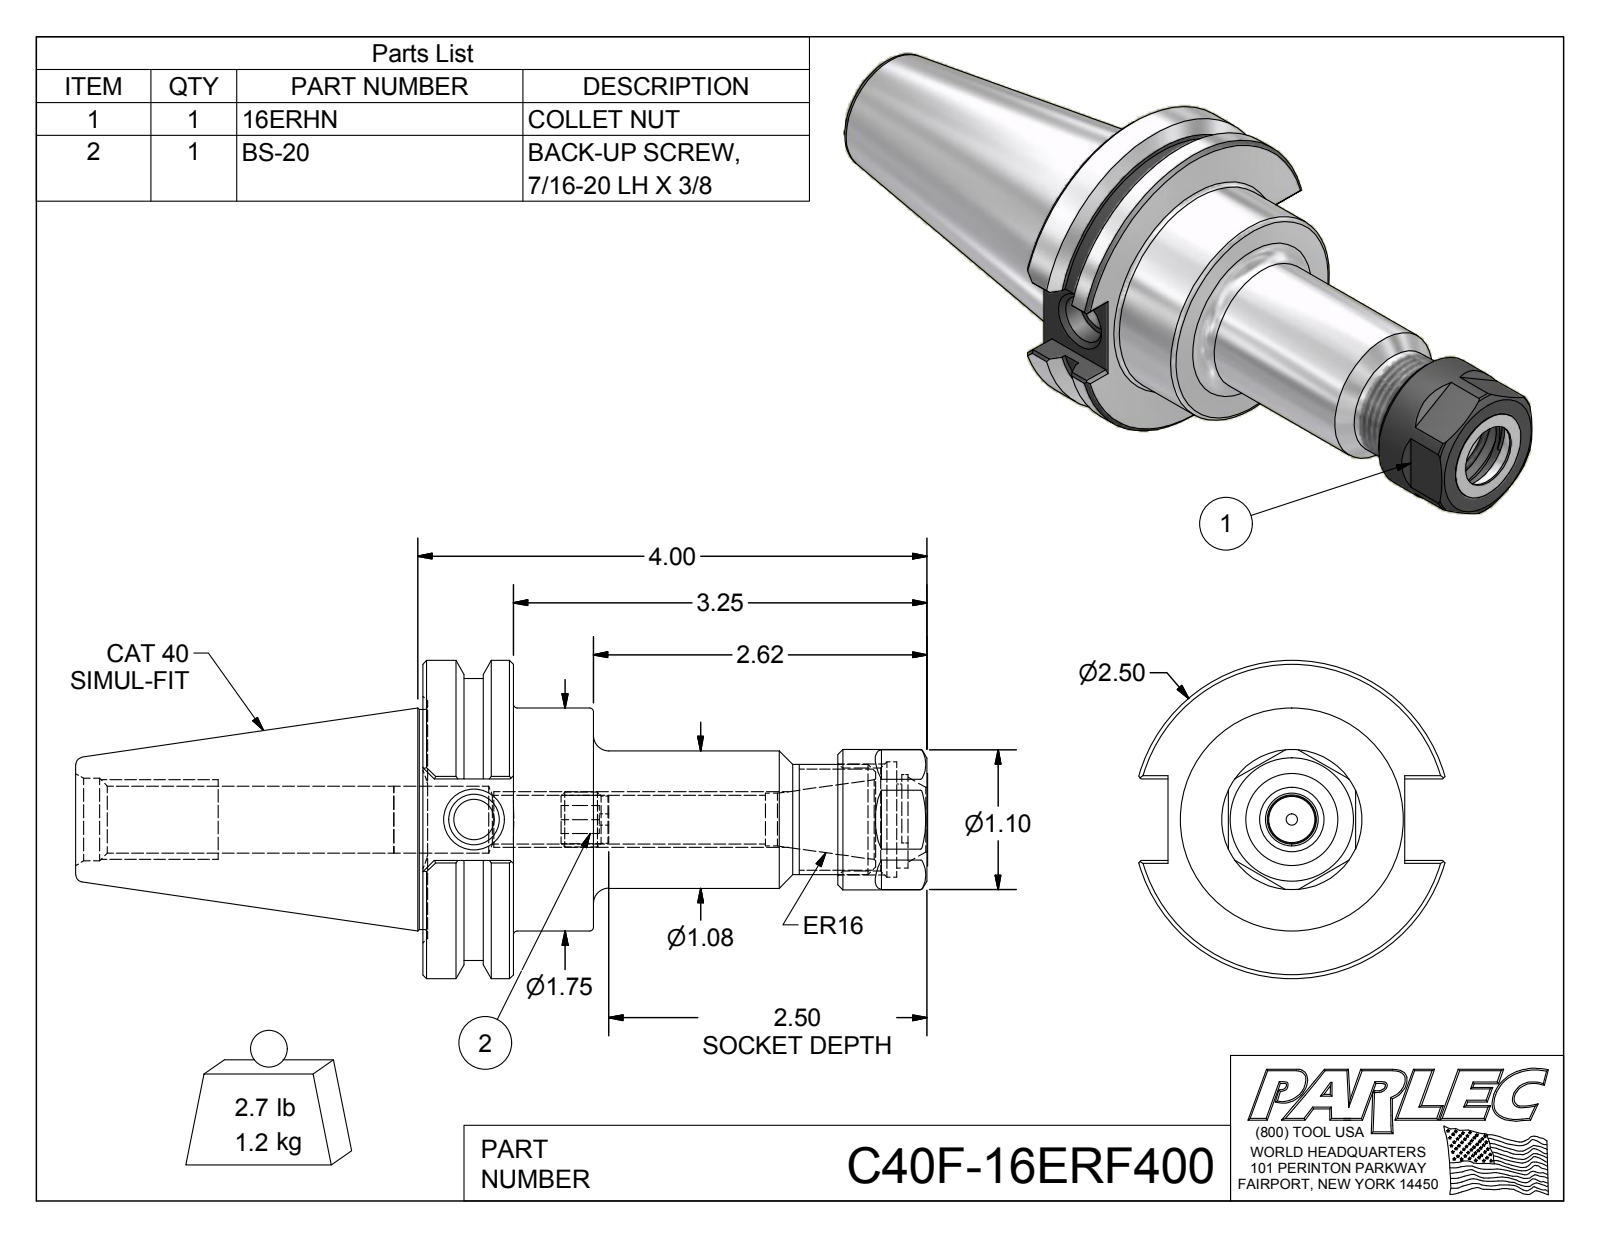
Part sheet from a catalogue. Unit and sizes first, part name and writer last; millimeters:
Units: millimetres
Overall size (bounding box): 169.86 × 63.5 × 61.11
Round holes (diameter × count): ⌀2.29 ×1, ⌀8 ×1, ⌀9.73 ×1, ⌀10.13 ×1, ⌀11.18 ×1, ⌀12.4 ×1, ⌀13.38 ×1, ⌀13.39 ×1, ⌀16.46 ×1, ⌀17.02 ×1, ⌀20.5 ×1, ⌀23 ×1
Round bosses / shafts (diameter × count): ⌀63.5 ×1, ⌀56.26 ×1, ⌀44.45 ×1, ⌀28 ×1, ⌀27.43 ×1, ⌀22 ×1, ⌀10.97 ×1, ⌀9.46 ×1
Partial cylindrical surfaces — rounded edges, fillets, slot ends (radius × count): R7.24 ×1, R9 ×1
Main face-to-face distances: 18.04, 34.04, 16, 100.59, 82.55, 66.55, 25.15, 94.89, 76.85, 60.85
Hole centre spacings: 1.52
Volume: 156 607 mm³ · Surface area: 33 409 mm²
Bodies: 3 solids, 129 faces (59 planar, 26 cylindrical, 44 other)
Part name (STEP PRODUCT): C40F-16ER4-1; 16ERHN; BS-20; C40F-16ERF400
STEP written by: Autodesk Inventor 2016 (AUTOMOTIVE_DESIGN)
